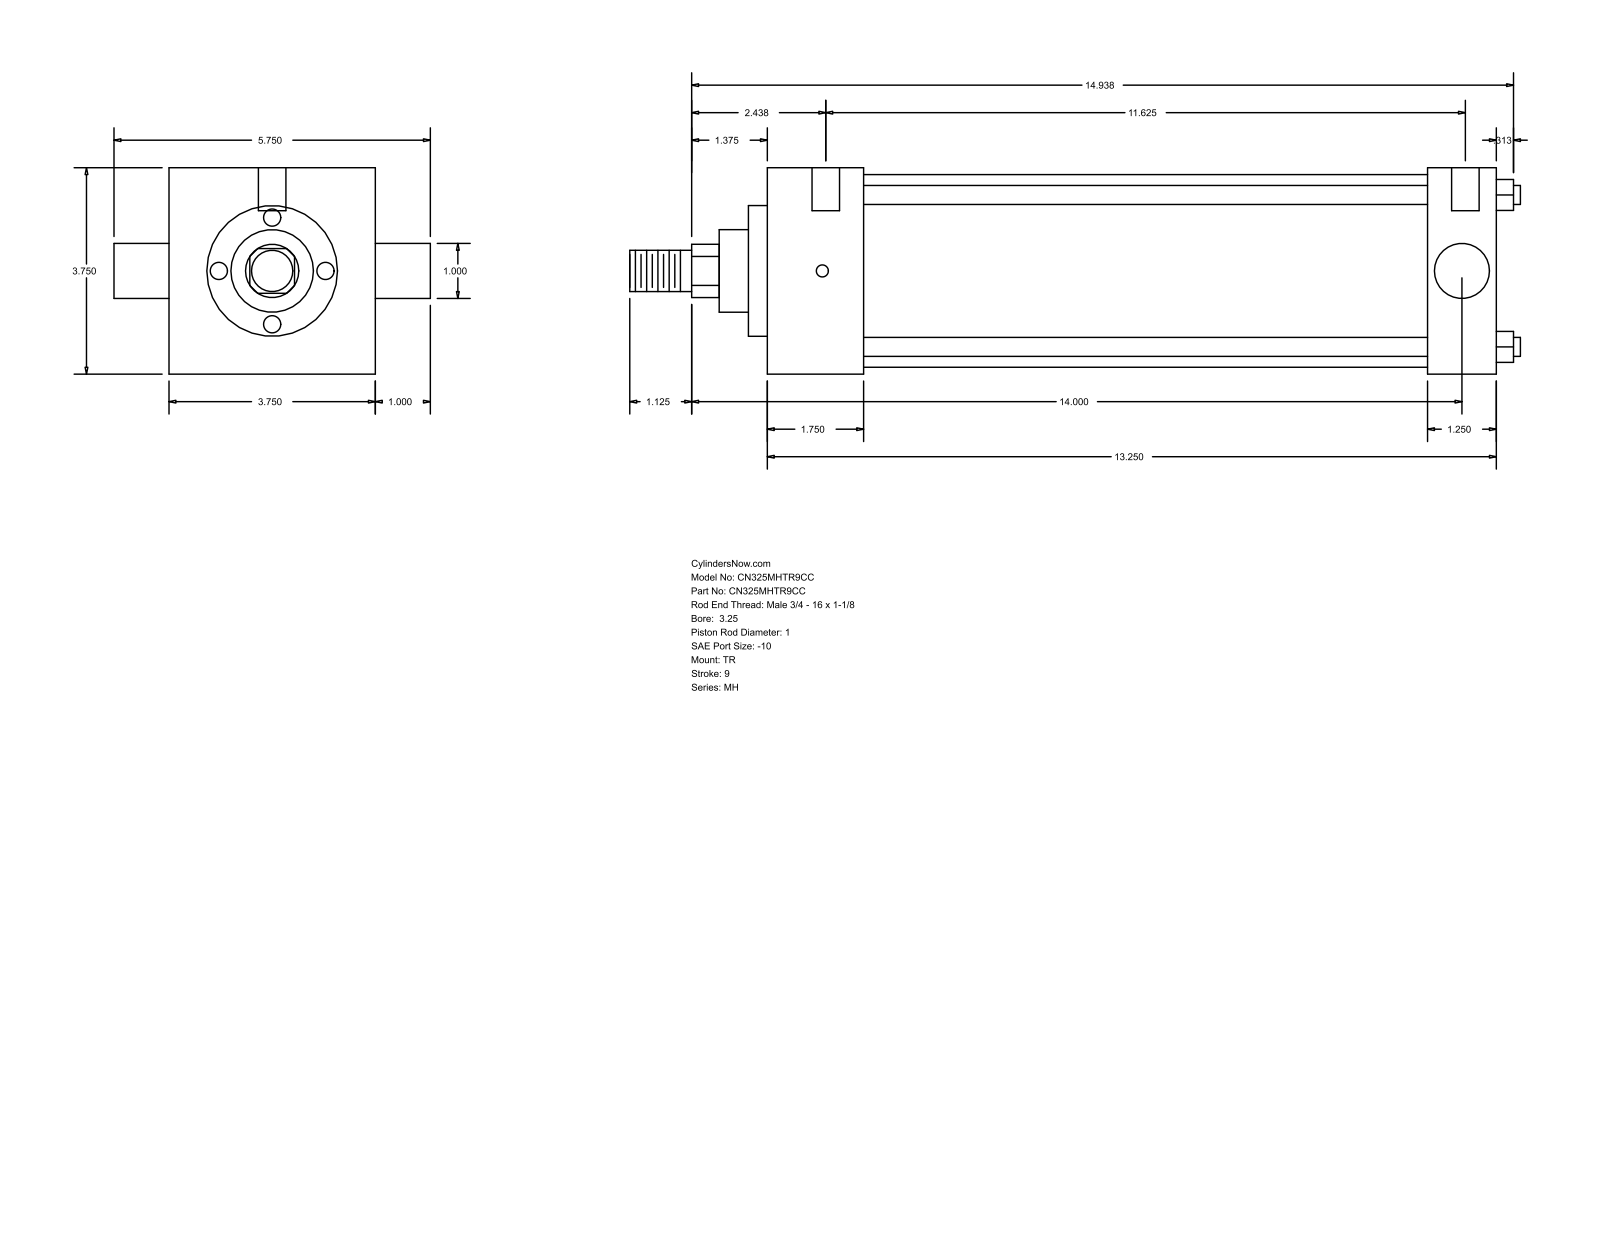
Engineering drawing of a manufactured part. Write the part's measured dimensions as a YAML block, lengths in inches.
part_name: "MH_TR__0325_1"
step_written_by: "GSSL Pune (CONFIG_CONTROL_DESIGN)"
units: inches
bodies: {solids: 0, faces: 86, planar: 61, cylindrical: 25, other: 0}
overall_size: [16.187, 5.75, 3.75]
round_holes:
  - {diameter: 0.219, count: 3}
  - {diameter: 0.5, count: 2}
round_bosses_or_shafts:
  - {diameter: 0.345, count: 4}
  - {diameter: 1, count: 2}
  - {diameter: 3.5, count: 1}
  - {diameter: 2.375, count: 1}
  - {diameter: 1.5, count: 1}
  - {diameter: 0.75, count: 1}
partial_cylinders:
  - {radius: 0.484, count: 1}
face_to_face_distances: [3.75, 13.25, 1.75, 12, 10.25, 11.5, 1.25, 0.344, 2.094, 12.344]
hole_center_spacings: [0.062, 0.187, 11.625, 11.687, 11.813, 11.875]
